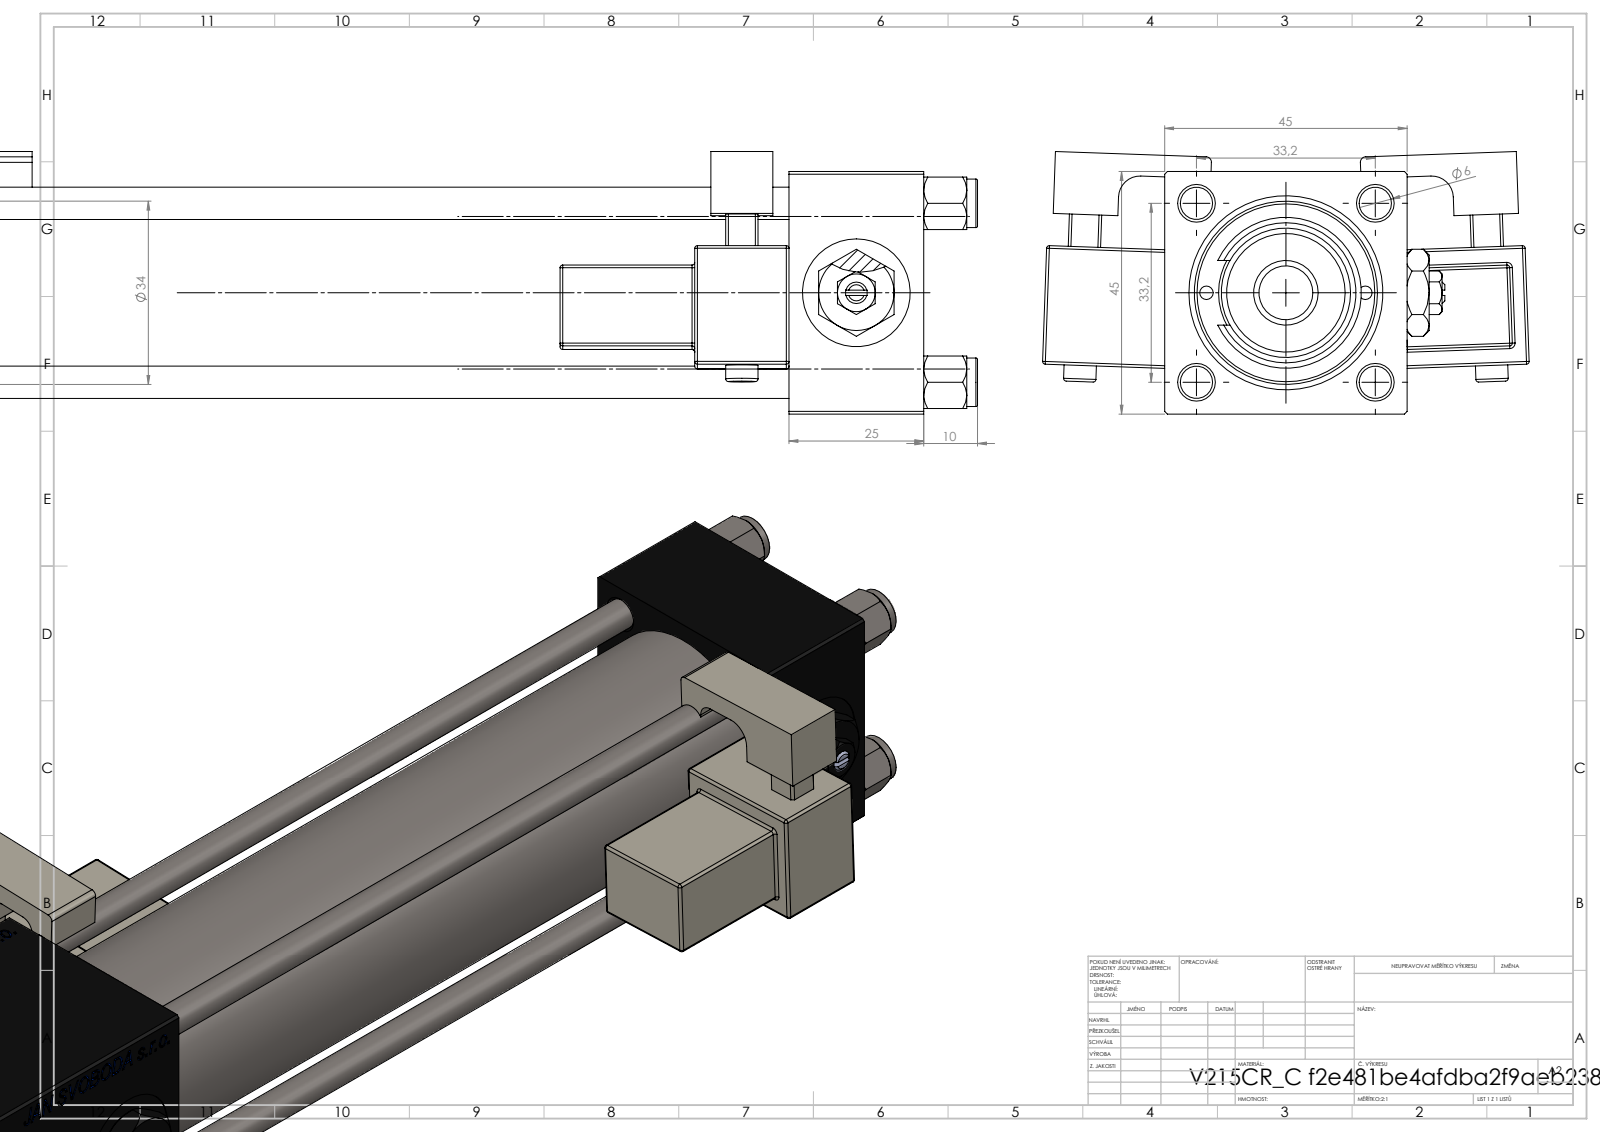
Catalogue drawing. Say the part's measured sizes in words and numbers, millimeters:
The part is named "FEMALE_PART_FOR_DFA; MFA; NUT_M5_C; V215CR_C_TYCINKA (+5 more)". Its 3-D file was written by "SolidWorks 2019 (CONFIG_CONTROL_DESIGN)". It is 17 solids with 1497 faces: 664 planar, 175 cylindrical and 658 other. Overall it measures 324 by 90.31 by 48.72 millimeters. Its volume is 353 102 cubic millimeters and its surface area 130 796 square millimeters. Round holes: 4 of diameter 6, 2 of diameter 2.5, 2 of diameter 7, 2 of diameter 13.16, 2 of diameter 20, 1 of diameter 10.5, 1 of diameter 22, 1 of diameter 24, 1 of diameter 25, 1 of diameter 32, 1 of diameter 33. Round bosses or shafts: 4 of diameter 9, 2 of diameter 6, 1 of diameter 38, 1 of diameter 34, 1 of diameter 28, 1 of diameter 18, 1 of diameter 12, 1 of diameter 11. Partial cylindrical surfaces (rounded edges, fillets, slot ends): 48 of radius 0.5, 2 of radius 1, 2 of radius 2.5, 2 of radius 4, 1 of radius 9.75, 1 of radius 10.5. The main face-to-face distances are 45, 25, 3, 180, 155, 228, 22.99, 44.8, 14.5, 13. The hole center spacings are 16.7, 23.48, 33.2, 35.47, 14.75, 46.95, 29.5, 180.5.
